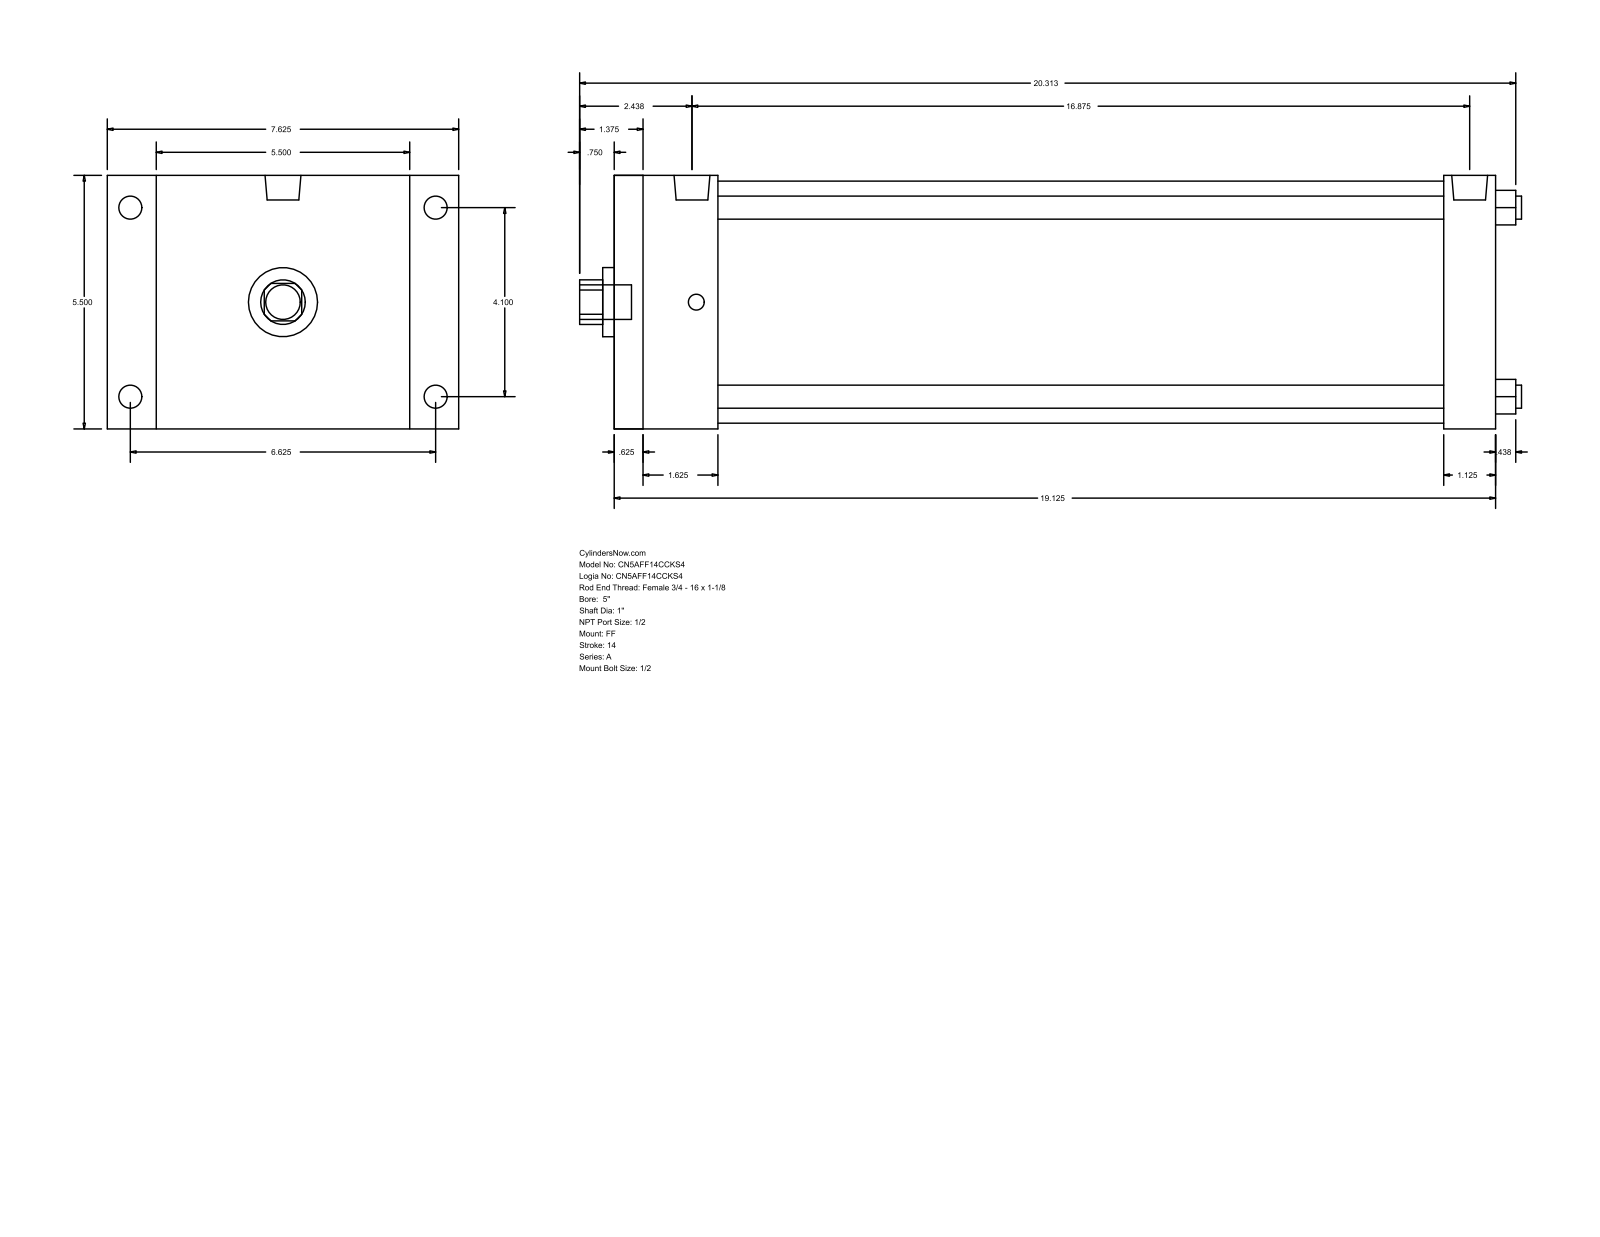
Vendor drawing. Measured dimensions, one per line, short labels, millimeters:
name: A_FF__0500_1
written by: GSSL Pune (CONFIG_CONTROL_DESIGN)
unit: mm
bodies: 0 solids, 92 faces (64 planar, 28 cylindrical, 0 other)
size: 519.11 × 193.68 × 139.7
holes: 4× ⌀12.7, 1× ⌀25.4, 1× ⌀38.1, 1× ⌀133.35
bosses: 4× ⌀12.7, 4× ⌀8.73, 2× ⌀19.77, 1× ⌀19.05
rounds: 1× R12.29
face distances: 139.7, 485.77, 15.87, 469.9, 28.57, 457.2, 441.33, 57.15, 41.28, 400.05
hole spacings: 73.64, 104.14, 147.28
